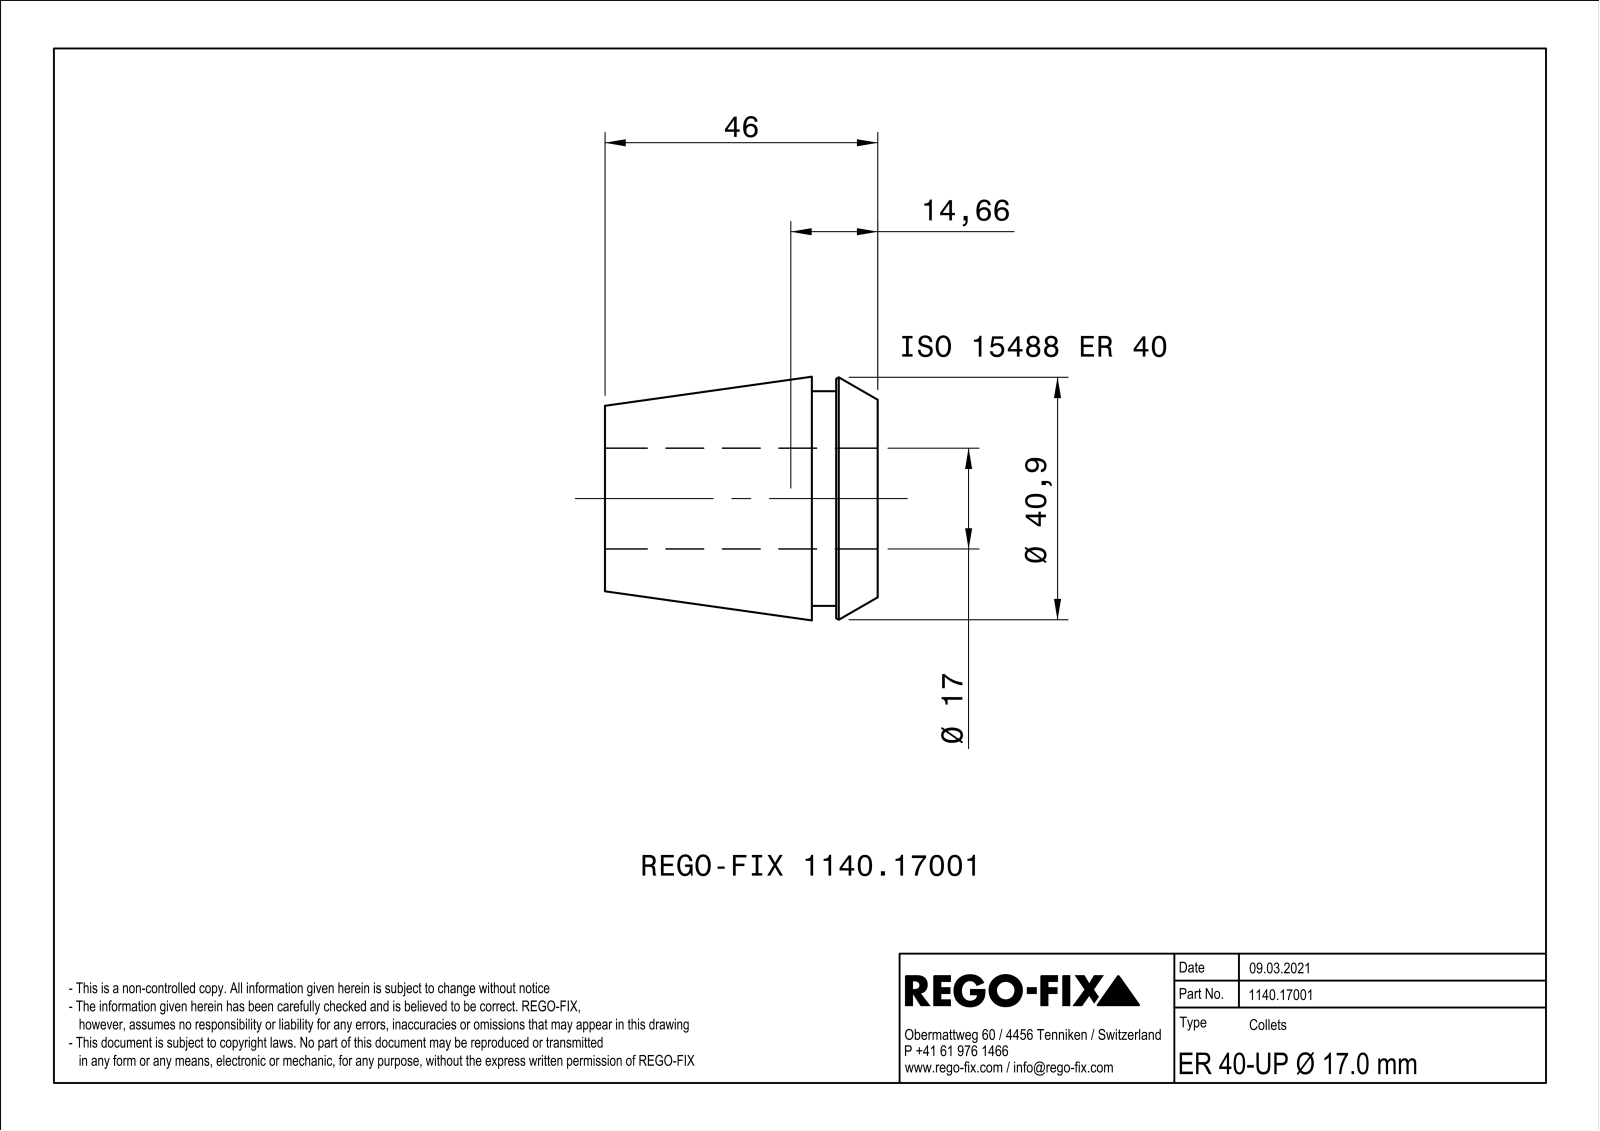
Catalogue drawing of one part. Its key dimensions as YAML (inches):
part_name: "NOCUT"
step_written_by: "SIEMENS PLM Software Solid Edge ST10 (AUTOMOTIVE_DESIGN)"
units: inches
bodies: {solids: 1, faces: 177, planar: 88, cylindrical: 9, other: 80}
overall_size: [1.811, 1.614, 1.614]
volume: 1.898
surface_area: 32.2
round_holes:
  - {diameter: 0.669, count: 1}
round_bosses_or_shafts:
  - {diameter: 1.425, count: 1}
face_to_face_distances: [0.039, 1.811, 0.437, 1.374, 0.276, 0.161, 1.535, 0.295, 0.02, 0.142]
